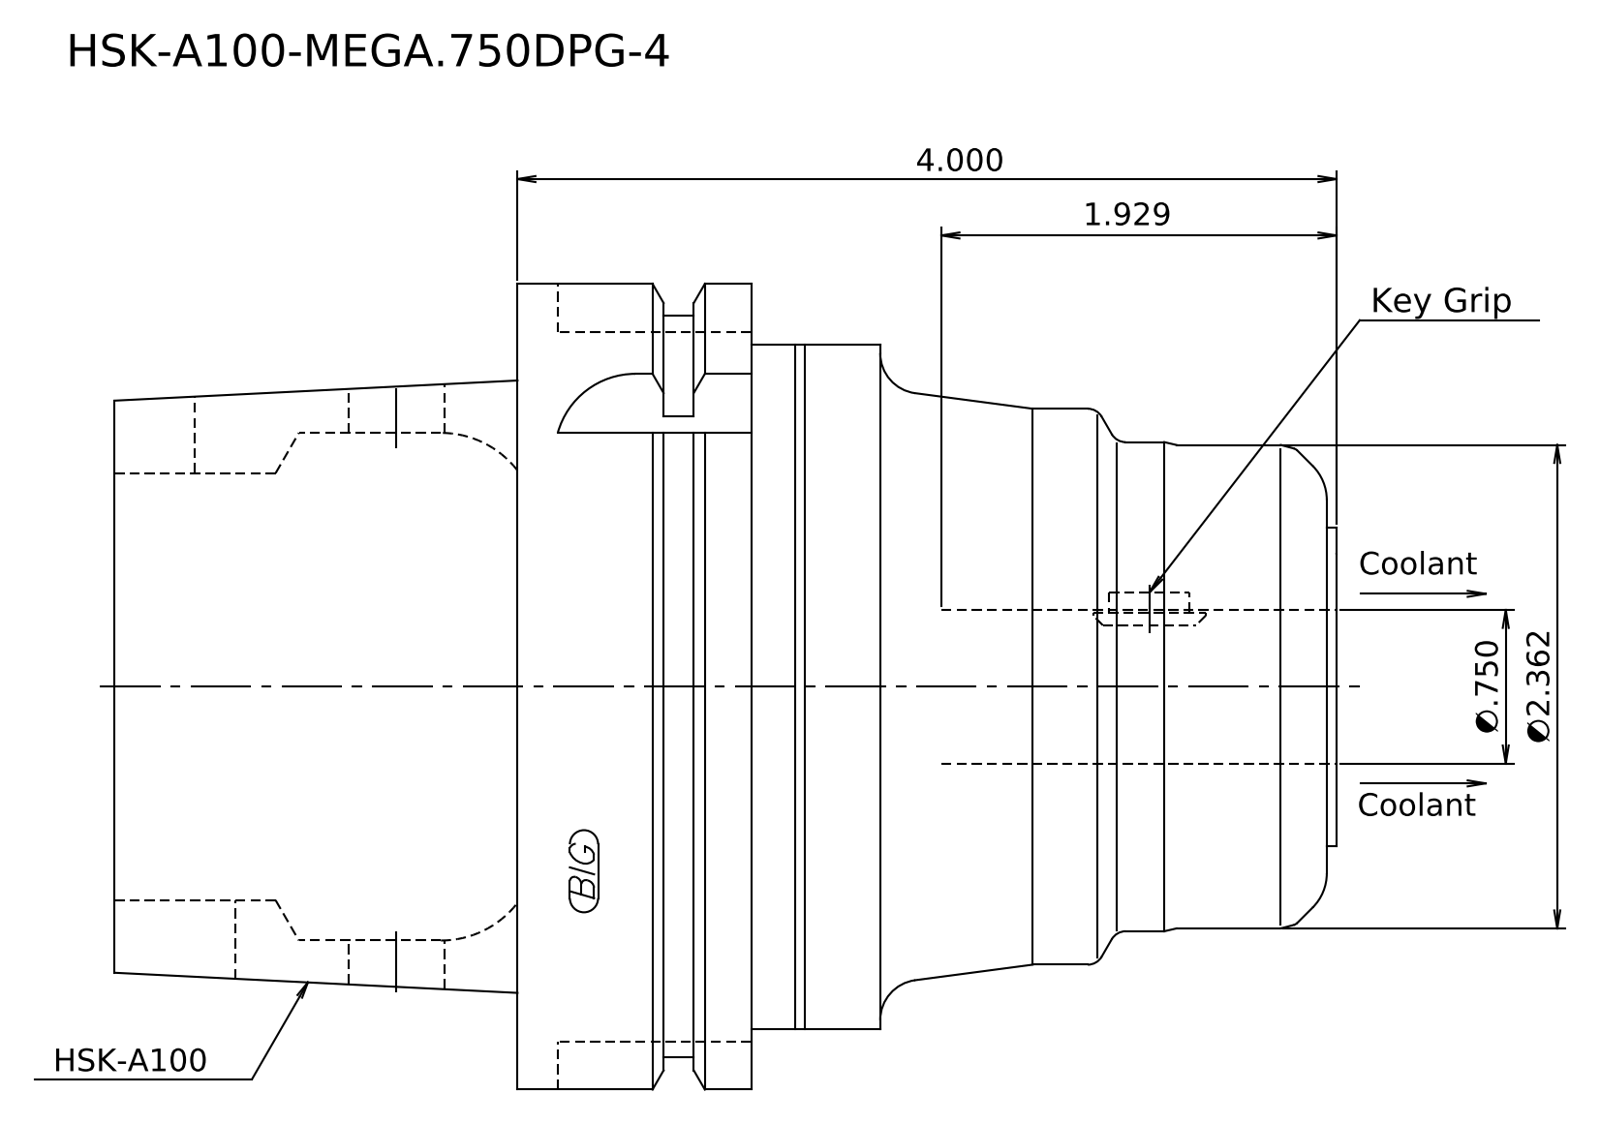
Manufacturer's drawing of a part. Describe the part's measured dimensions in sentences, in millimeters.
Its 3-D file was written by "Kubotek KeyCreator 2011 V10.0.2 (22737) (automotive_design)". It is 1 solid with 25 faces: 8 planar, 8 cylindrical and 9 other. Overall it measures 151.6 by 100 by 100 millimeters. Its volume is 715 442 cubic millimeters and its surface area 51 327 square millimeters. Round bosses or shafts: 1 of diameter 100, 1 of diameter 92, 1 of diameter 85, 1 of diameter 69, 1 of diameter 60.7, 1 of diameter 60, 1 of diameter 39.56. The main face-to-face distances are 50, 29, 79, 72.6, 101.6, 151.6, 1.2, 71.4, 100.4, 150.4.
